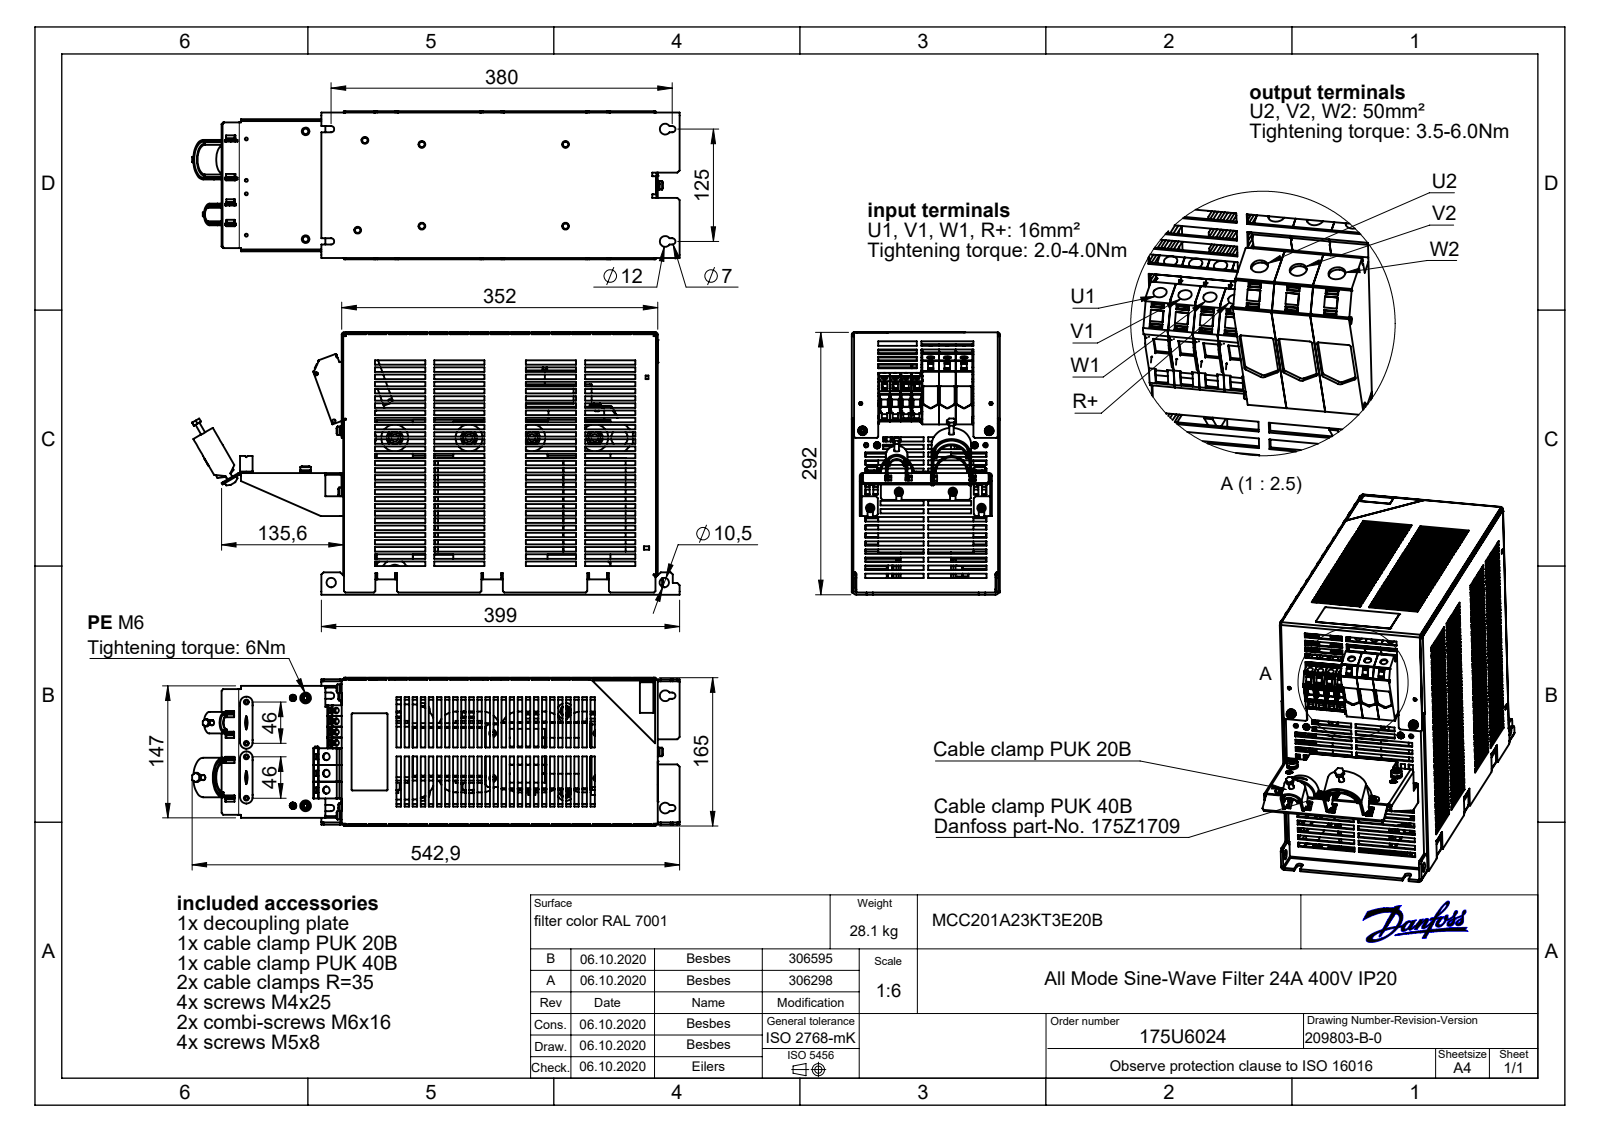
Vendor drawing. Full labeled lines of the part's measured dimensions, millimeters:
Part name (STEP PRODUCT): 125864; Tx-Schraube M8x85 ISO 14583 4.8 vz_Tx-Schraube M8x85 ISO 14583 4.8 vz; Tx-Schraube M5x8 ISO 14583 4.8 vz_Tx-Schraube M5x8 ISO 14583 4.8 vz; 131797 (+8 more)
STEP written by: SolidWorks 2018 (AUTOMOTIVE_DESIGN)
Units: millimetres
Bodies: 131 solids, 7794 faces (5204 planar, 1840 cylindrical, 750 other)
Overall size (bounding box): 542.9 × 292.1 × 165
Volume: 5 079 000 mm³ · Surface area: 1 774 000 mm²
Round holes (diameter × count): ⌀5 ×14, ⌀4.2 ×11, ⌀4.5 ×11, ⌀8 ×11, ⌀3.5 ×10, ⌀3.3 ×8, ⌀6 ×8, ⌀6.3 ×8, ⌀6.8 ×8, ⌀7.95 ×8, ⌀8.2 ×8, ⌀11 ×8
Round bosses / shafts (diameter × count): ⌀18 ×12, ⌀1 ×10, ⌀5 ×9, ⌀16 ×8, ⌀10 ×8, ⌀9.5 ×7, ⌀8 ×7, ⌀7 ×7
Partial cylindrical surfaces — rounded edges, fillets, slot ends (radius × count): R0.3 ×250, R1 ×77, R3 ×23, R5.5 ×22, R3.5 ×19, R2.5 ×18, R0.25 ×16, R2 ×13
Main face-to-face distances: 1.5, 54.5, 109, 53, 56, 163.5, 110.5, 2.5, 2, 107.5
Hole centre spacings: 12, 24.19, 70, 18.6, 21.01, 24, 31.89, 38.58
